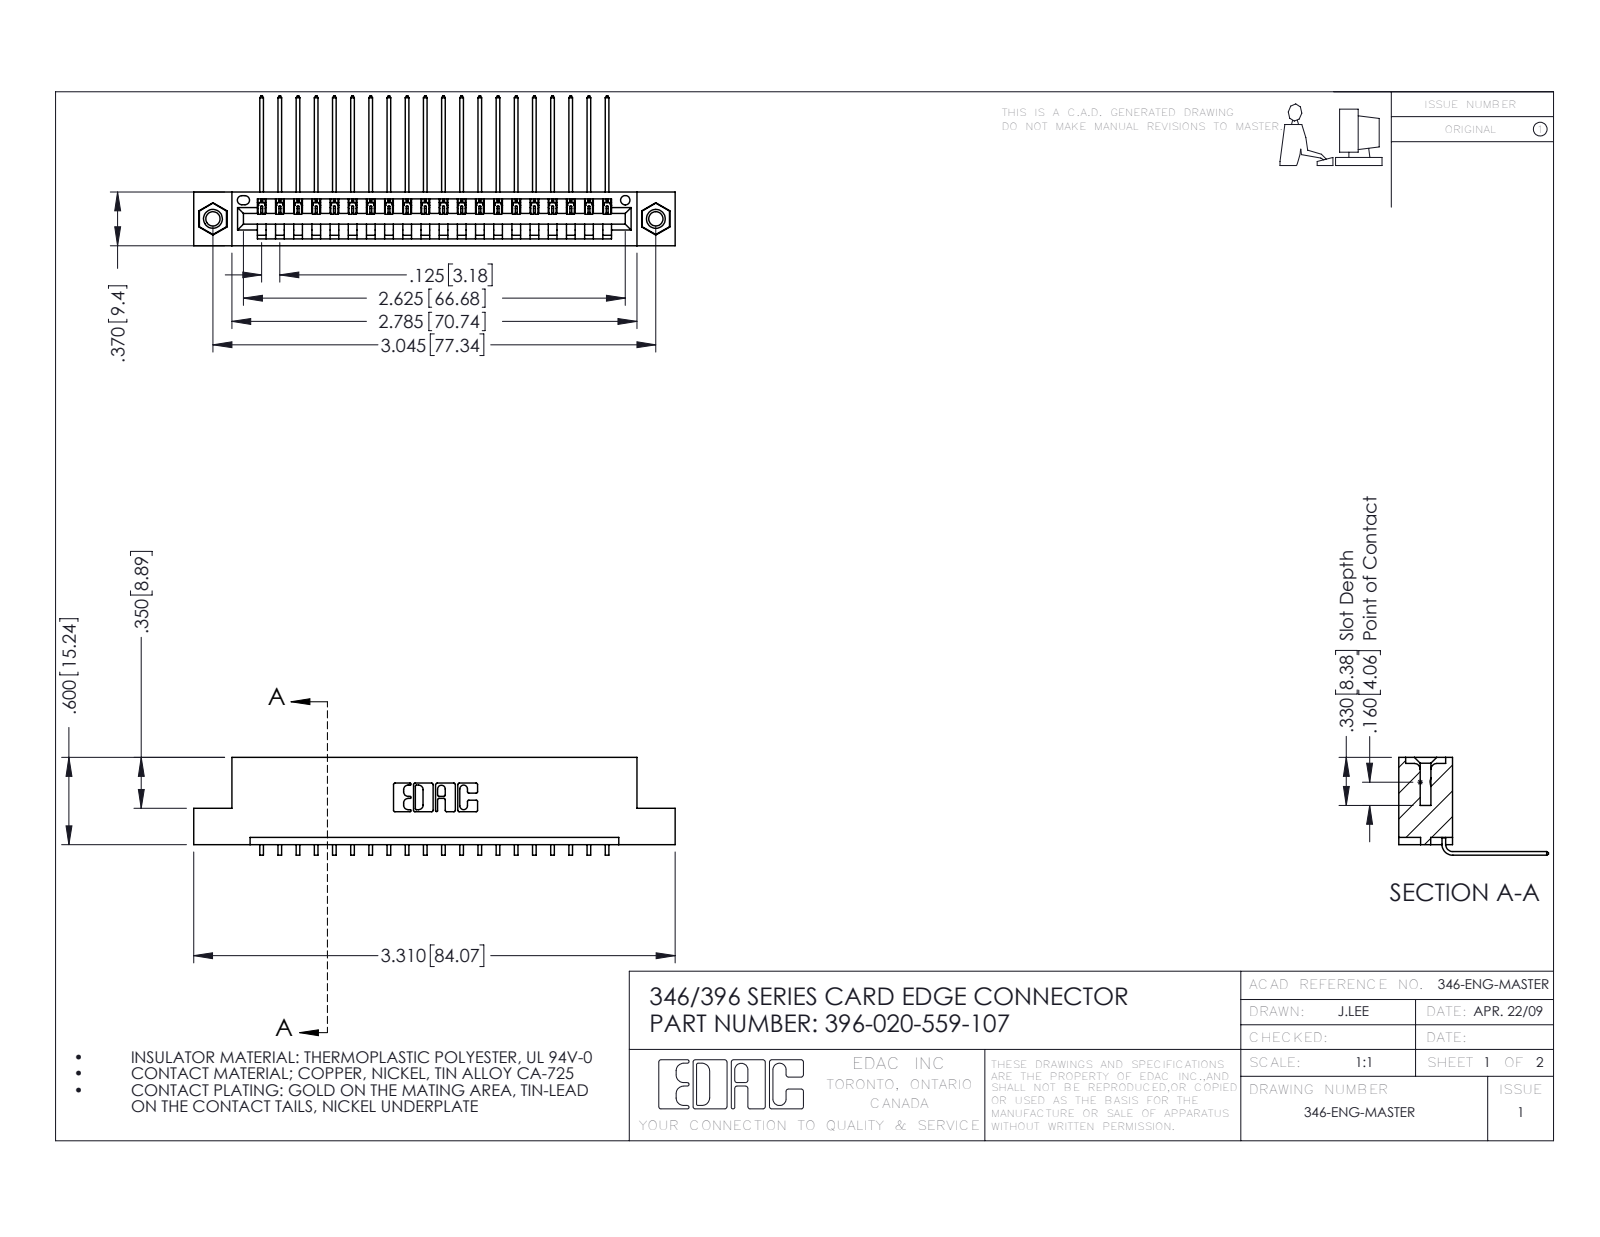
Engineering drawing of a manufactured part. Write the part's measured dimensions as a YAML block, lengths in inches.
part_name: "346 Part_Flush Mounting Lugs - 0.156 Dia-TI; 345-292-001_558 559 Tail - 1; 345-250-001_345-250-005-103; 396-020-559-107"
step_written_by: "SolidWorks 2016 (CONFIG_CONTROL_DESIGN)"
units: inches
bodies: {solids: 23, faces: 1382, planar: 948, cylindrical: 418, other: 16}
overall_size: [3.31, 1.03, 0.673]
volume: 0.485
surface_area: 15.7
round_holes:
  - {diameter: 0.098, count: 2}
  - {diameter: 0.125, count: 2}
  - {diameter: 0.156, count: 2}
  - {diameter: 0.064, count: 1}
round_bosses_or_shafts:
  - {diameter: 0.155, count: 2}
partial_cylinders:
  - {radius: 0.006, count: 40}
  - {radius: 0.01, count: 22}
  - {radius: 0.007, count: 6}
  - {radius: 0.031, count: 6}
  - {radius: 0.026, count: 3}
  - {radius: 0.031, count: 2}
  - {radius: 0.04, count: 2}
  - {radius: 0.014, count: 1}
face_to_face_distances: [0.048, 0.322, 0.37, 0.25, 0.072, 0.025, 0.298, 0.148, 0.222, 0.1]
hole_center_spacings: [0.246, 2.837, 3.045]
